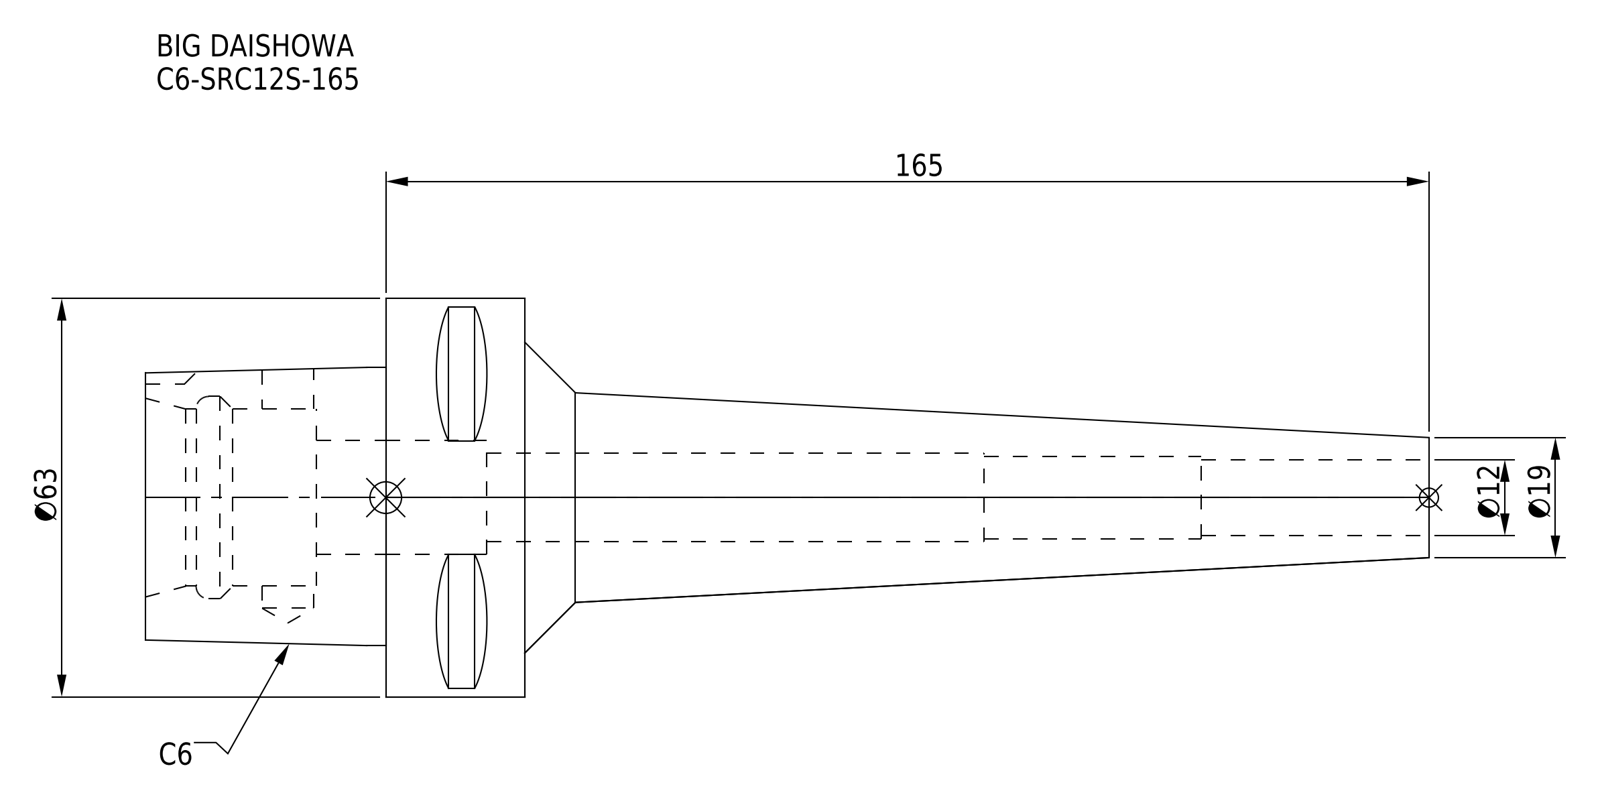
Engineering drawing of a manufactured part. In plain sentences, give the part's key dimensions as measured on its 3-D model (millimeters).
The part is named "C6-SRC12S-165". Its 3-D file was written by "CREO PARAMETRIC BY PTC INC, 2016380 (AUTOMOTIVE_DESIGN)". It is 1 solid with 65 faces: 30 planar, 21 cylindrical and 14 other. Overall it measures 203 by 63 by 63 millimeters. Its volume is 160 481 cubic millimeters and its surface area 37 065 square millimeters. Round holes: 1 of diameter 8.1, 1 of diameter 12, 1 of diameter 13, 1 of diameter 14, 1 of diameter 18, 1 of diameter 28, 1 of diameter 32. Round bosses or shafts: 1 of diameter 63. Partial cylindrical surfaces (rounded edges, fillets, slot ends): 1 of radius 5. The main face-to-face distances are 22, 60, 38, 27, 33, 11, 24.89, 55.4, 143, 165.
